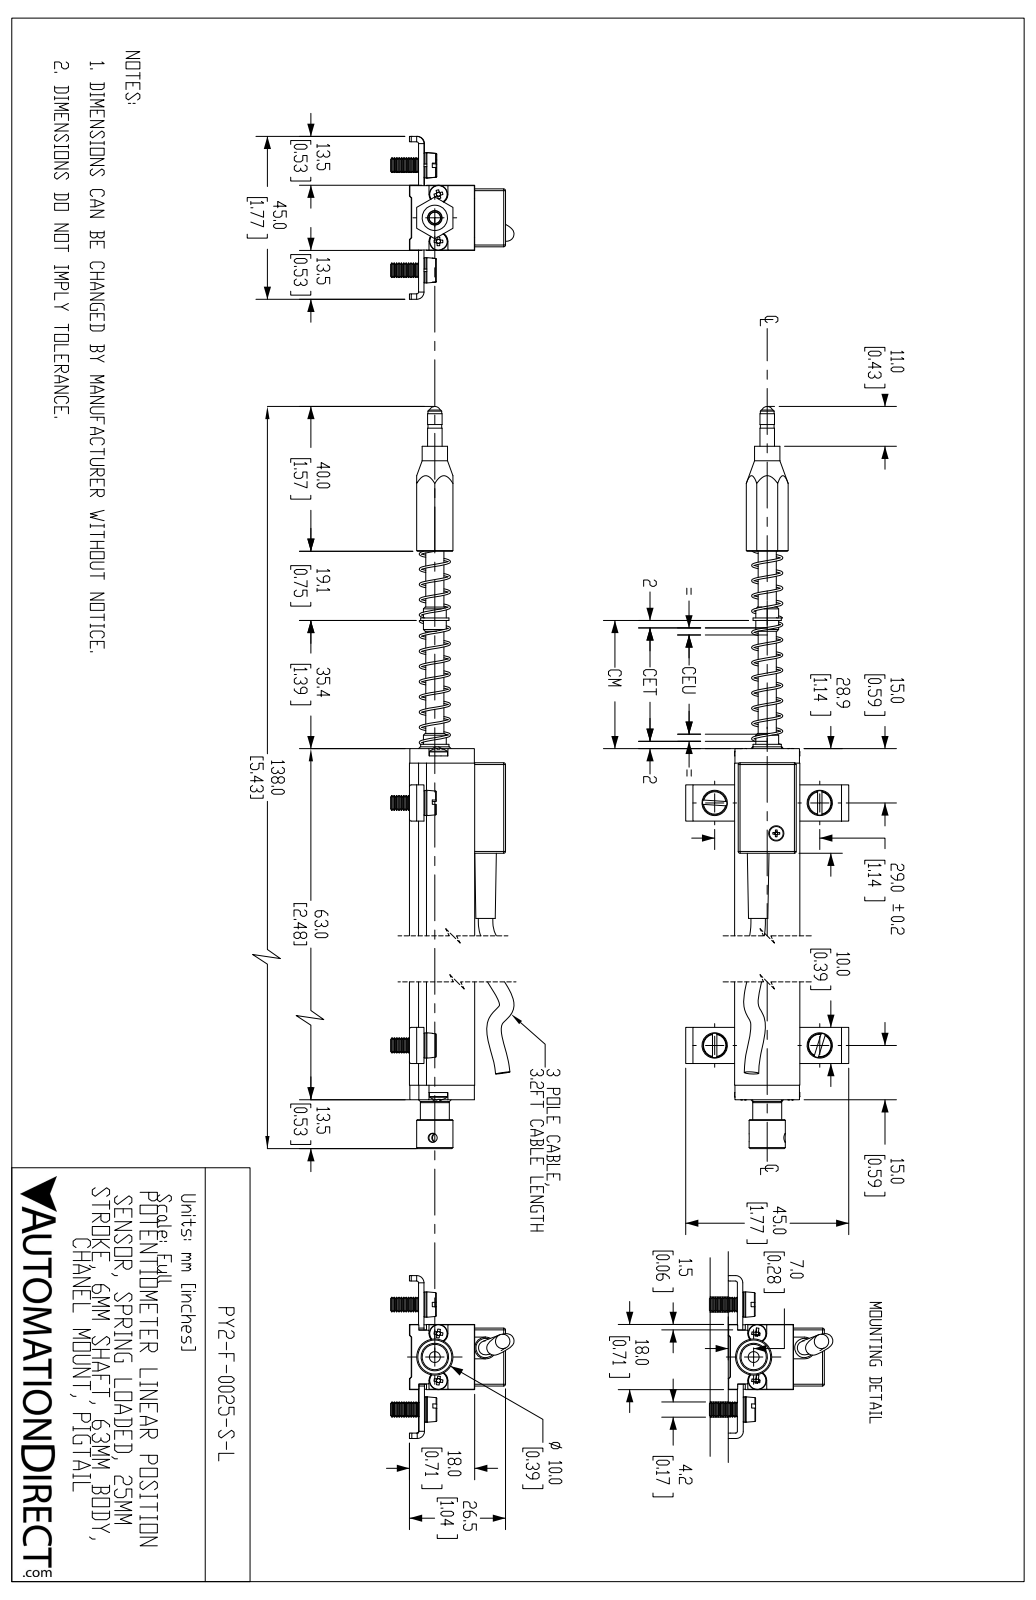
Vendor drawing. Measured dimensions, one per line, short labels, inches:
name: PY2-F-0025-S-L
written by: SolidWorks 2019 (AUTOMOTIVE_DESIGN)
unit: in
bodies: 31 solids, 969 faces (323 planar, 247 cylindrical, 399 other)
size: 5.606 × 1.772 × 1.34
volume: 1.73 in³; area: 29.99 in²
holes: 4× ⌀0.142, 4× ⌀0.169, 2× ⌀0.091, 2× ⌀0.098, 2× ⌀0.106, 2× ⌀0.236, 1× ⌀0.063, 1× ⌀0.079, 1× ⌀0.081, 1× ⌀0.083, 1× ⌀0.102, 1× ⌀0.13
bosses: 6× ⌀0.157, 4× ⌀0.274, 3× ⌀0.197, 3× ⌀0.098, 2× ⌀0.15, 1× ⌀0.394, 1× ⌀0.315, 1× ⌀0.307
rounds: 25× R0.02, 4× R0.079, 2× R0.102, 1× R0.177
face distances: 0.709, 0.059, 0.079, 0.02, 0.157, 0.61, 0.039, 0.689, 2.323, 2.165
hole spacings: 0.259, 0.574, 1.142, 1.299, 1.477, 1.73, 0.406, 0.512
